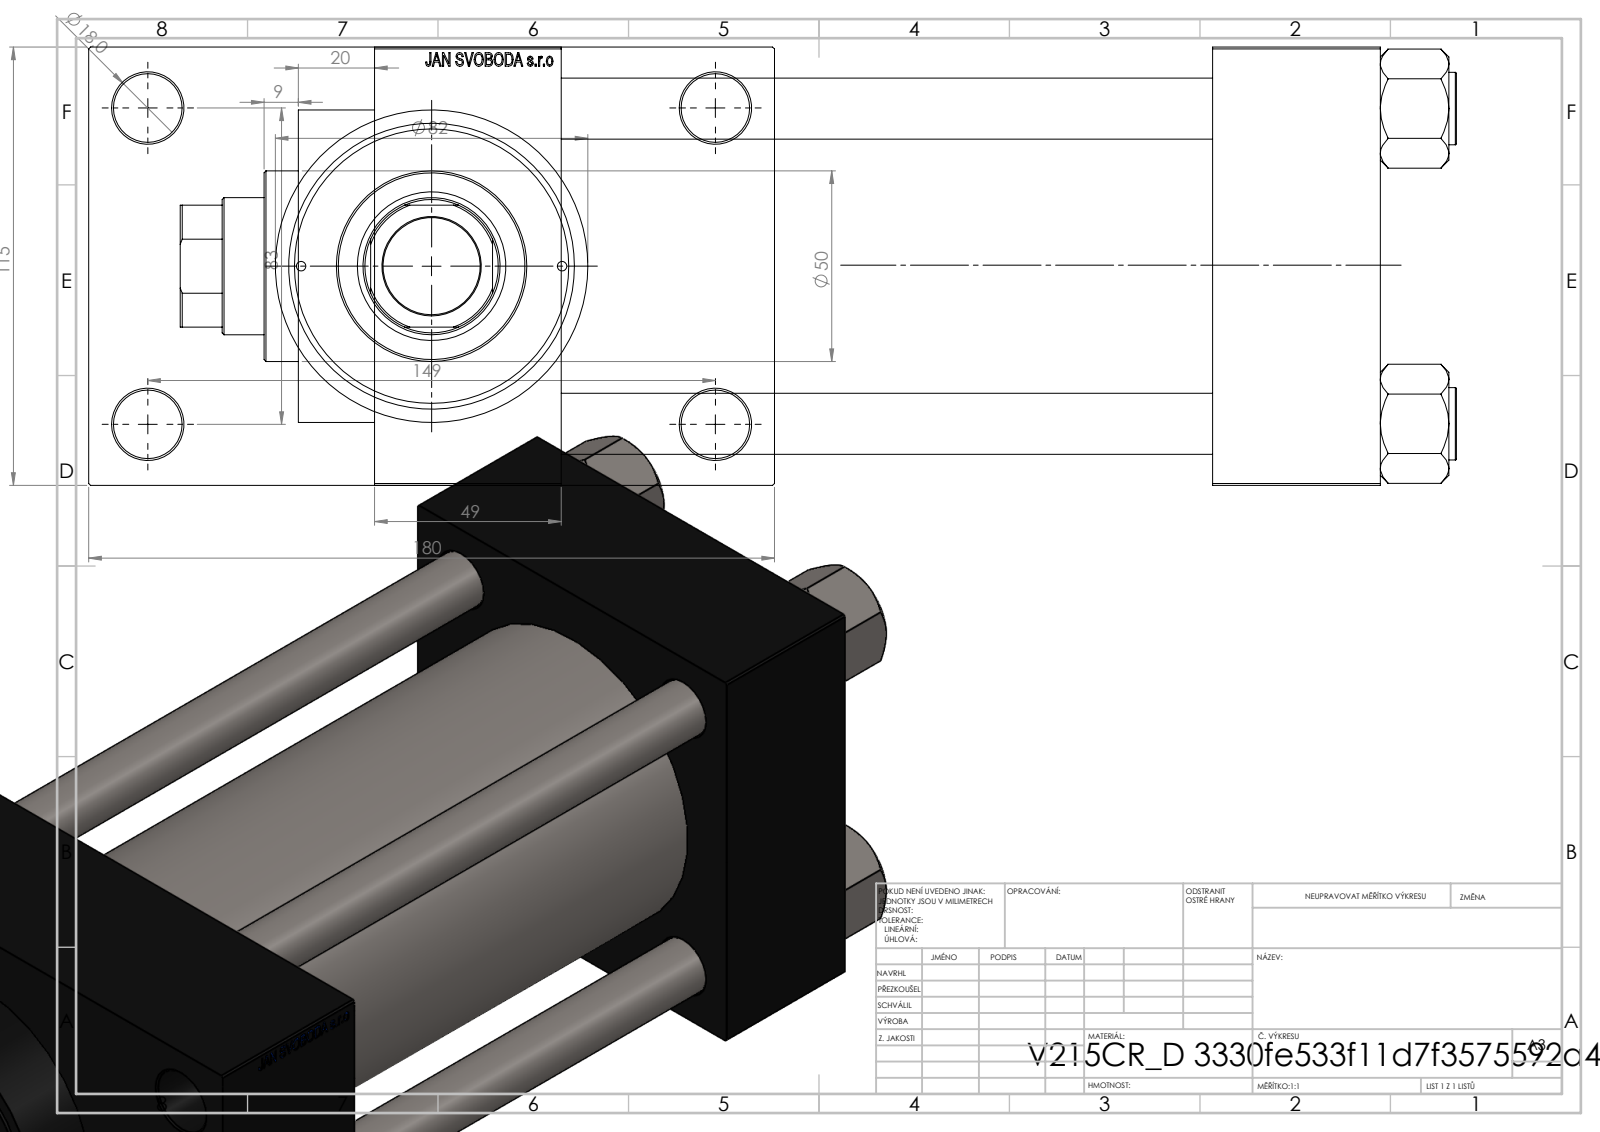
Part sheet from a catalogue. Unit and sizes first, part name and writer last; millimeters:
Units: millimetres
Overall size (bounding box): 335 × 180 × 115
Round holes (diameter × count): ⌀16 ×4, ⌀18 ×4, ⌀2.5 ×2, ⌀7 ×2, ⌀26.44 ×2, ⌀35 ×2, ⌀25.5 ×1, ⌀36 ×1, ⌀39 ×1, ⌀61 ×1, ⌀72 ×1, ⌀80 ×1
Round bosses / shafts (diameter × count): ⌀19 ×4, ⌀86 ×1, ⌀82 ×1, ⌀50 ×1
Partial cylindrical surfaces — rounded edges, fillets, slot ends (radius × count): R17.5 ×1
Main face-to-face distances: 115, 171, 220, 49, 44, 215, 264, 32.5, 147.5, 180
Hole centre spacings: 33.15, 41.96, 57.81, 58.48, 82.7, 85.28, 86.17, 89.24
Volume: 2 270 000 mm³ · Surface area: 381 525 mm²
Bodies: 11 solids, 1160 faces (547 planar, 93 cylindrical, 520 other)
Part name (STEP PRODUCT): V215CR_VCP_D; V215CR_D_Body; NUT_M5_D; V215CR_D_TYCINKA (+1 more)
STEP written by: SolidWorks 2019 (CONFIG_CONTROL_DESIGN)
